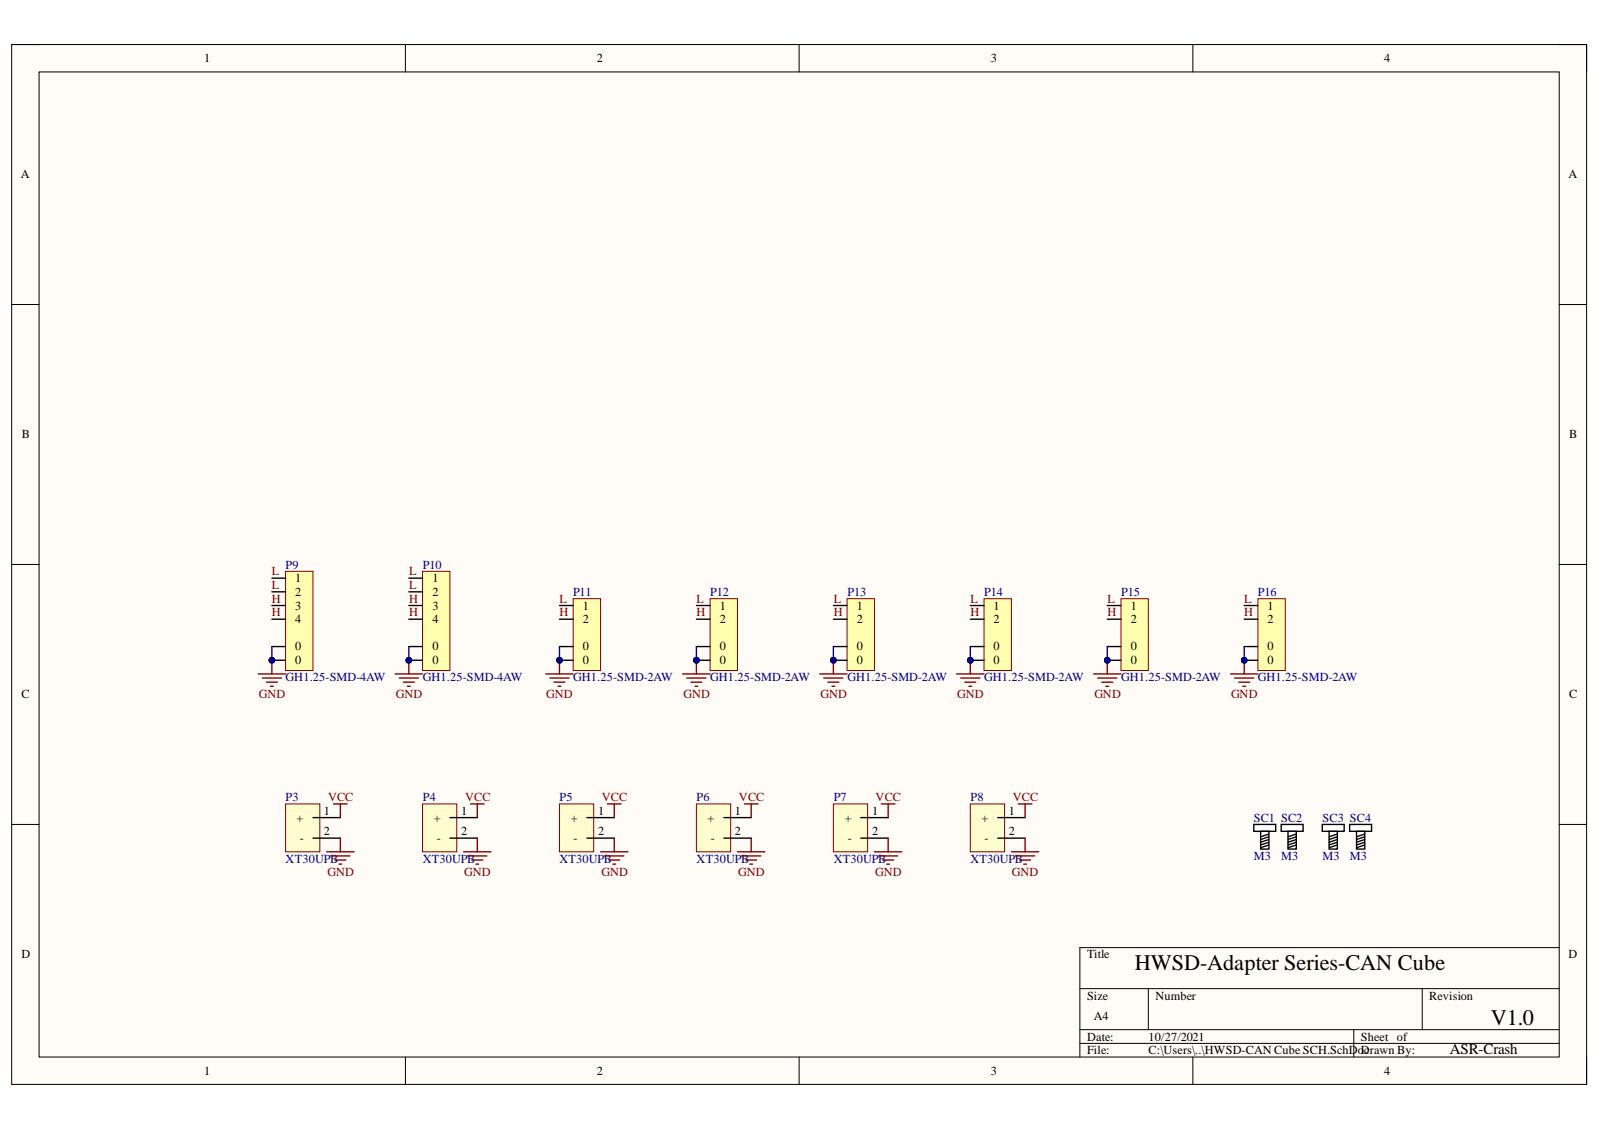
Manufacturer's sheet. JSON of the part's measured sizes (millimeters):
{"part_name": "PCB; Board; P16; JST_GH_BM02B-GHS-TBT_1x02-1MP_P1.25mm_Vertical (+7 more)", "step_written_by": "Open CASCADE 6.8 (AUTOMOTIVE_DESIGN)", "units": "millimeters", "bodies": {"solids": 19, "faces": 3508, "planar": 2788, "cylindrical": 304, "other": 416}, "overall_size": [50.13, 30.13, 11.4], "volume_mm3": 4638, "surface_area_mm2": 8746, "round_holes": [[1.8, 12], [2.2, 8], [2.6, 8], [2.5, 4], [3, 4]], "round_bosses_or_shafts": [[1.6, 12]], "partial_cylinders_radius": [[0.1, 55], [0.5, 36], [1, 16], [0.2, 12], [1.5, 12], [1.8, 12], [2.61, 3], [2.6, 1]], "face_to_face_distances": [1.69, 0.6, 5.2, 4.6, 4.2, 2.8, 9.4, 3.4, 0.5, 5.09], "hole_center_spacings": [5, 24.92, 29.28, 9.6, 28.66, 34.74, 34.73, 28.67]}
